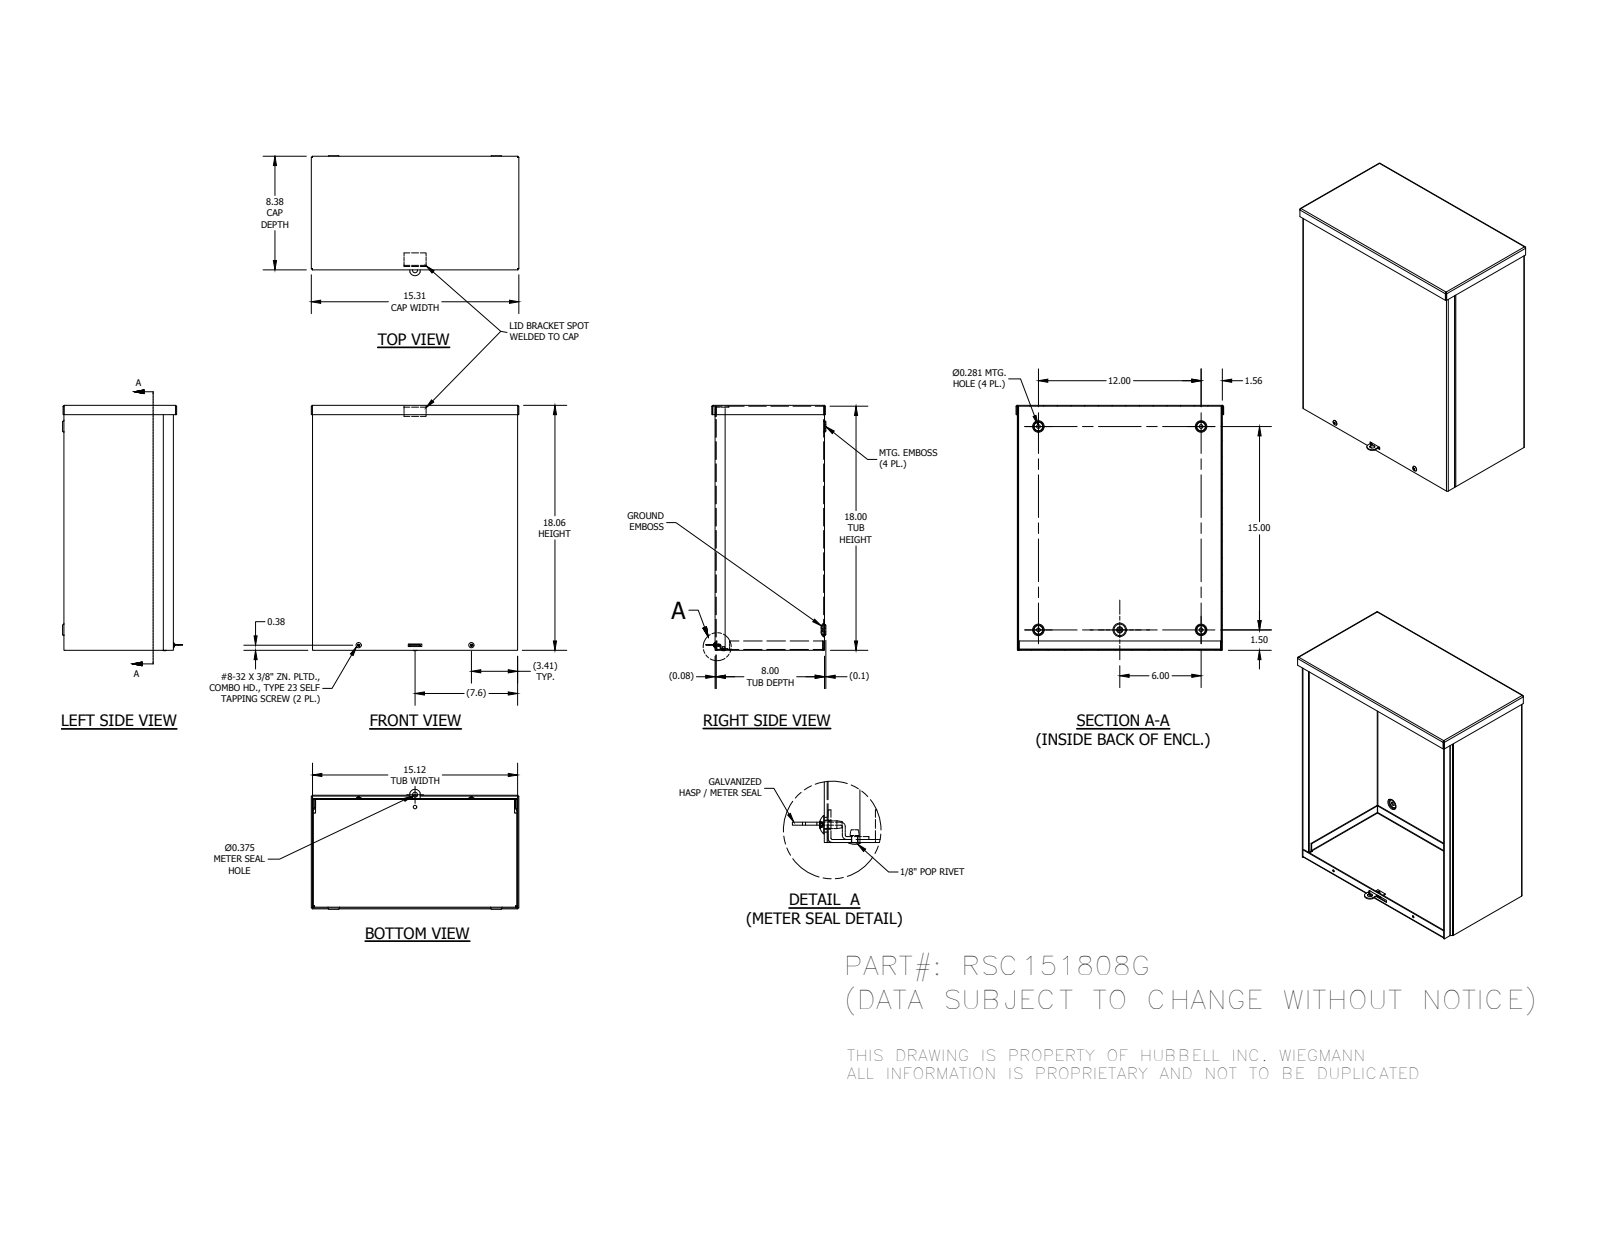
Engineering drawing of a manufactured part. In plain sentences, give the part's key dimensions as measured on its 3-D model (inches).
The part is named "RSC151808GBKPA; RSC1508GEWPA; RSC1518GLFA; RSC1508GCPA (+5 more)". Its 3-D file was written by "Autodesk Inventor 2014 (AUTOMOTIVE_DESIGN)". It is 9 solids with 320 faces: 183 planar, 61 cylindrical and 76 other. Overall it measures 18.102 by 15.311 by 8.85 inches. Its volume is 71.95 cubic inches and its surface area 2 339 square inches. Round holes: 4 of diameter 0.281, 4 of diameter 0.313, 2 of diameter 0.147, 1 of diameter 0.125, 1 of diameter 0.136, 1 of diameter 0.171, 1 of diameter 0.375. Round bosses or shafts: 2 of diameter 0.384, 2 of diameter 0.164, 1 of diameter 0.262, 1 of diameter 0.233, 1 of diameter 0.125. Partial cylindrical surfaces (rounded edges, fillets, slot ends): 19 of radius 0.031, 18 of radius 0.093, 1 of radius 0.105, 1 of radius 0.4. The main face-to-face distances are 0.062, 8.016, 15.062, 8.078, 7.954, 18, 15, 15.124, 18.062, 17.938. The hole center spacings are 2.16, 10.219, 4.306, 8.313, 16.23, 19.057, 6, 12.
